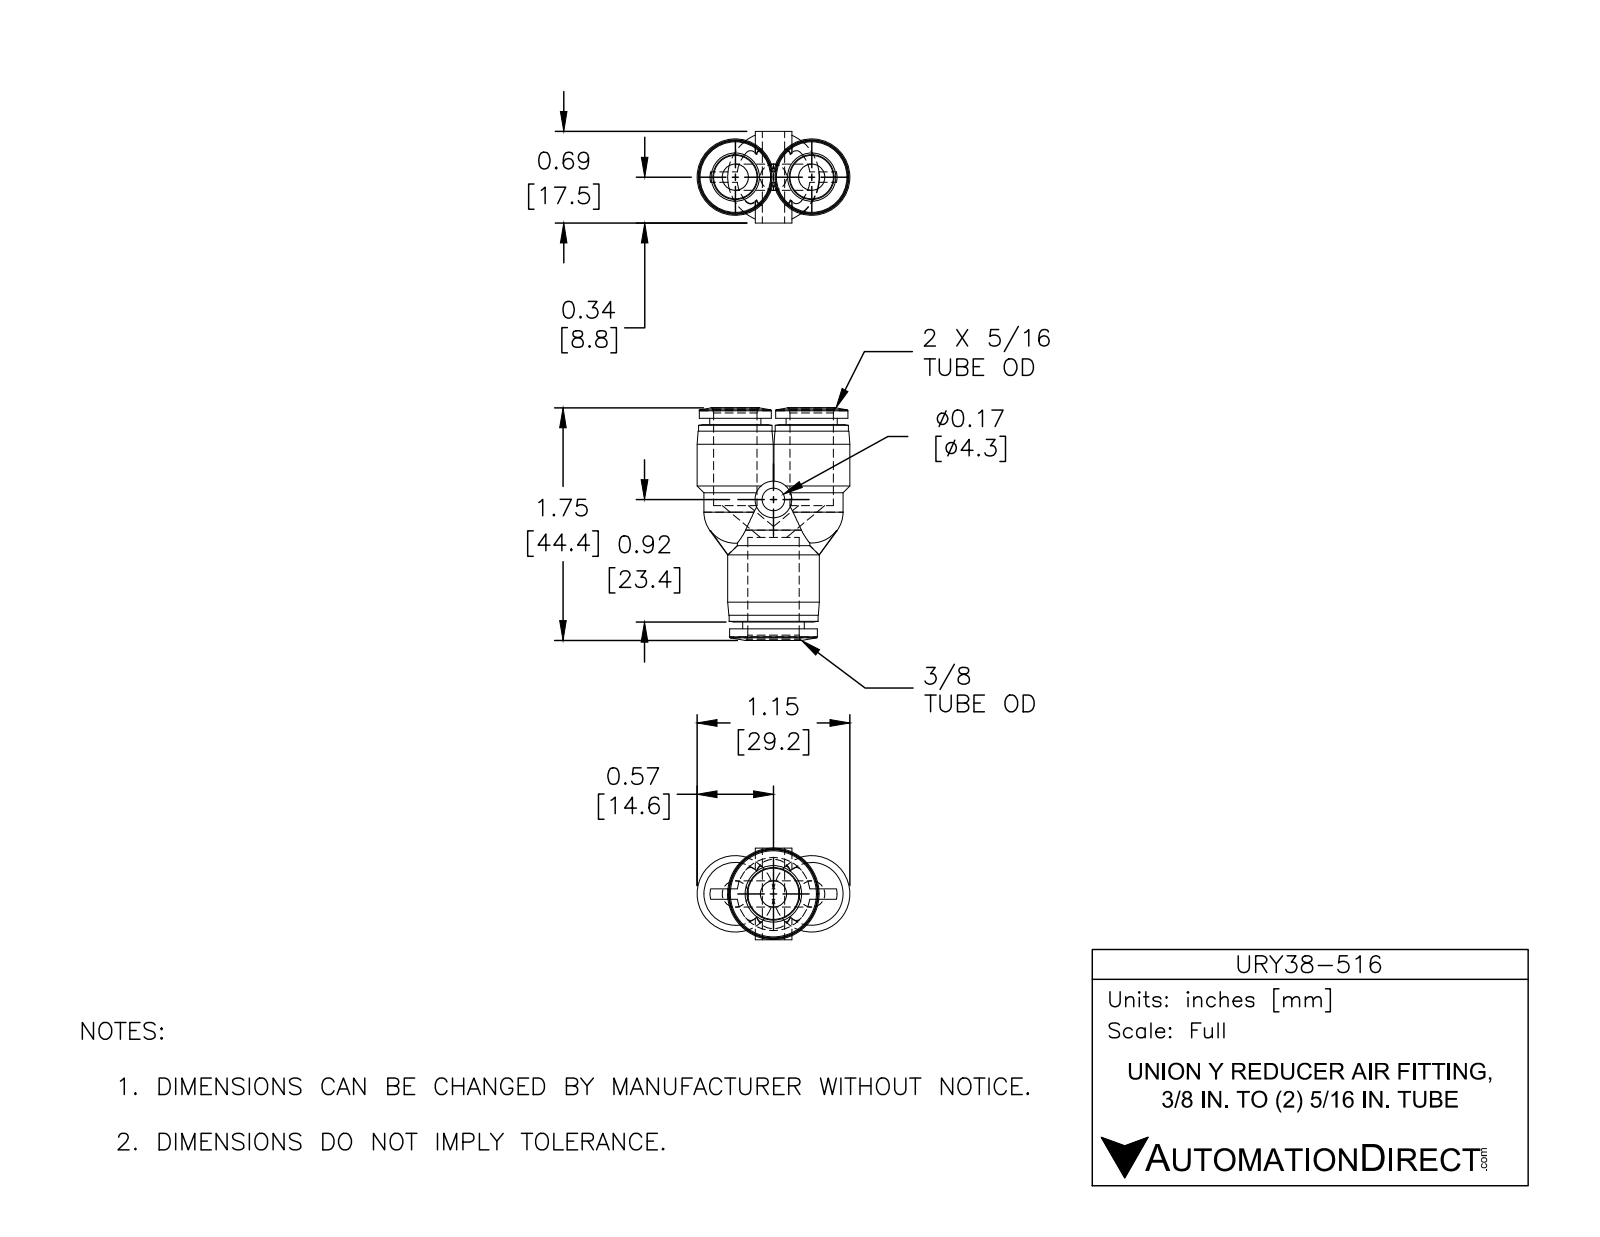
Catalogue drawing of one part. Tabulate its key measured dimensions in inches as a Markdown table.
| quantity | value |
| --- | --- |
| part name | URY38-516 |
| STEP written by | SolidWorks 2015 (CONFIG_CONTROL_DESIGN) |
| units | inches |
| bodies | 1 solid, 109 faces (19 planar, 40 cylindrical, 50 other) |
| overall size | 1.75 × 1.15 × 0.689 |
| volume | 0.478 in³ |
| surface area | 9.589 in² |
| round holes (diameter × count) | 0.327 × 2, 0.169 × 1, 0.386 × 1 |
| round bosses / shafts (diameter × count) | 0.551 × 3, 0.575 × 2, 0.543 × 2, 0.386 × 2, 0.689 × 1, 0.669 × 1, 0.661 × 1, 0.465 × 1 |
| partial cylindrical surfaces (radius × count) | 0.236 × 2 |
| main face-to-face distances | 1.585, 1.537, 0.047, 0.689, 0.051, 0.927, 0.61, 0.657, 0.876, 1.486 |
| hole center spacings | 0.287, 0.575 |
